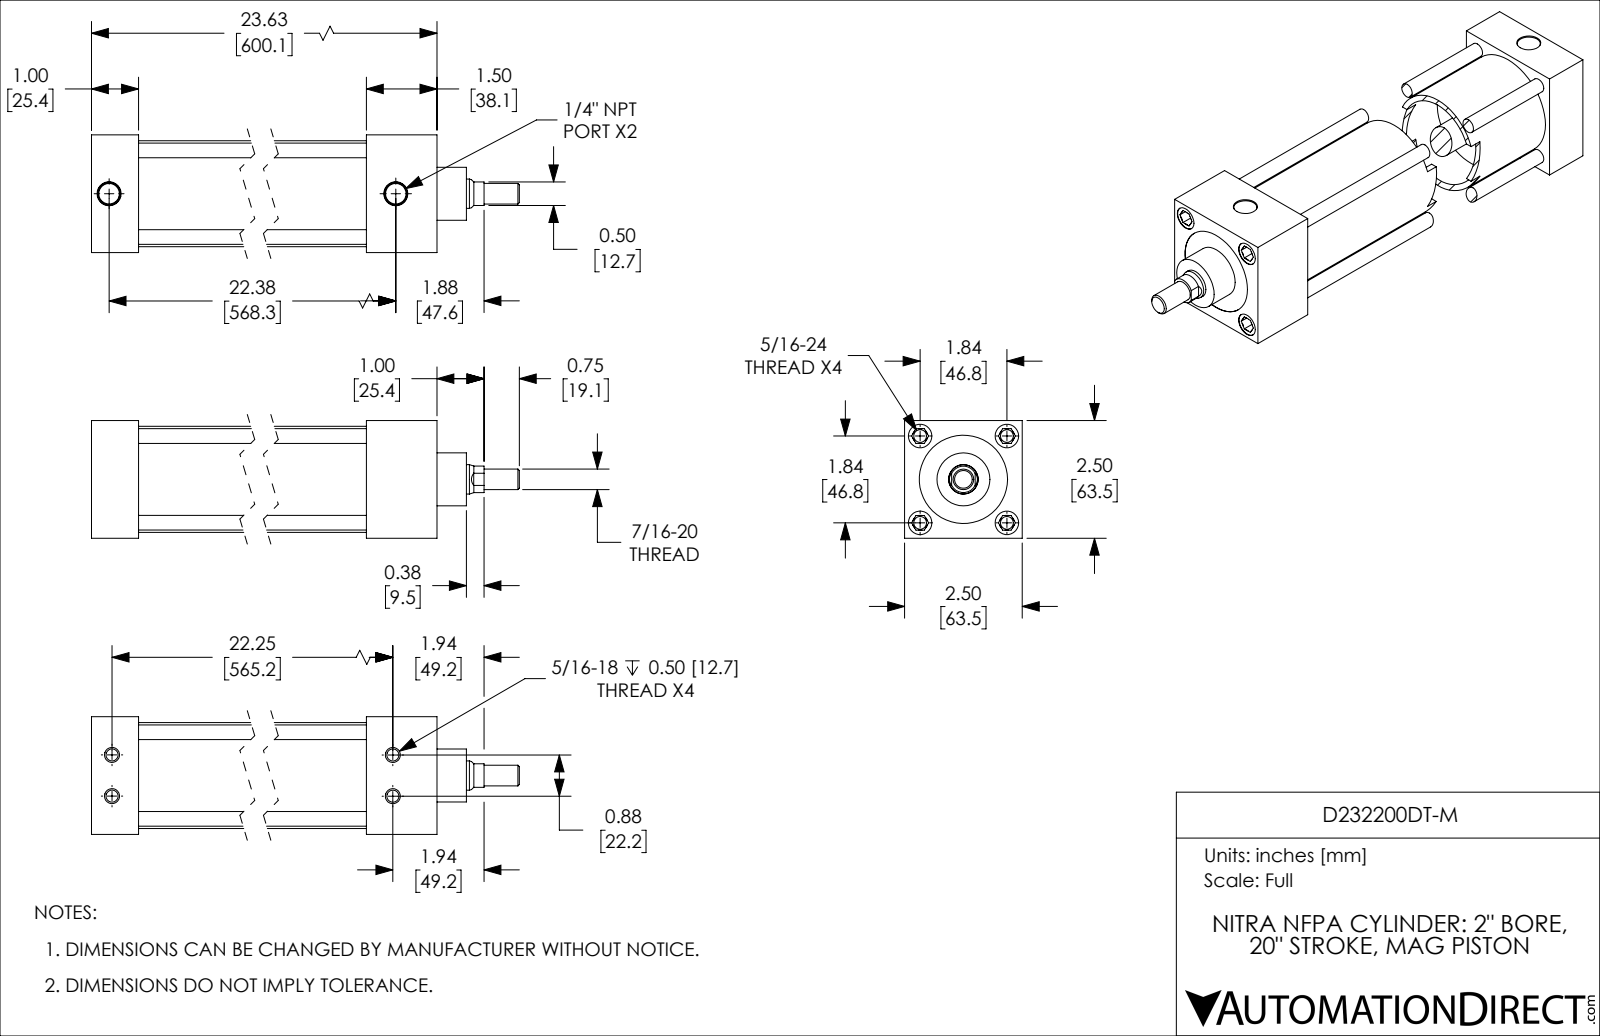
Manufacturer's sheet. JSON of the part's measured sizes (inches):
{"part_name": "D232200DT-M_BODY; D232200DT-M_PISTON_KK1; D232200DT-M", "step_written_by": "SolidWorks 2019 (CONFIG_CONTROL_DESIGN)", "units": "inches", "bodies": {"solids": 2, "faces": 200, "planar": 58, "cylindrical": 62, "other": 80}, "overall_size": [25.375, 2.5, 2.5], "volume_in3": 49.38, "surface_area_in2": 486.6, "round_holes": [[0.272, 7], [0.257, 4], [0.5, 4], [0.438, 2], [0.626, 1], [1.875, 1], [2.001, 1]], "round_bosses_or_shafts": [[0.312, 4], [2.251, 1], [1.999, 1], [1.125, 1], [0.624, 1], [0.437, 1]], "partial_cylinders_radius": [[0.281, 1]], "face_to_face_distances": [2.5, 1, 22.125, 21.125, 2.125, 1.125, 20, 23.625, 22.625, 21.5], "hole_center_spacings": [1.84, 1.844, 1.301, 0.441, 0.443, 0.875, 1.304, 2.602]}
